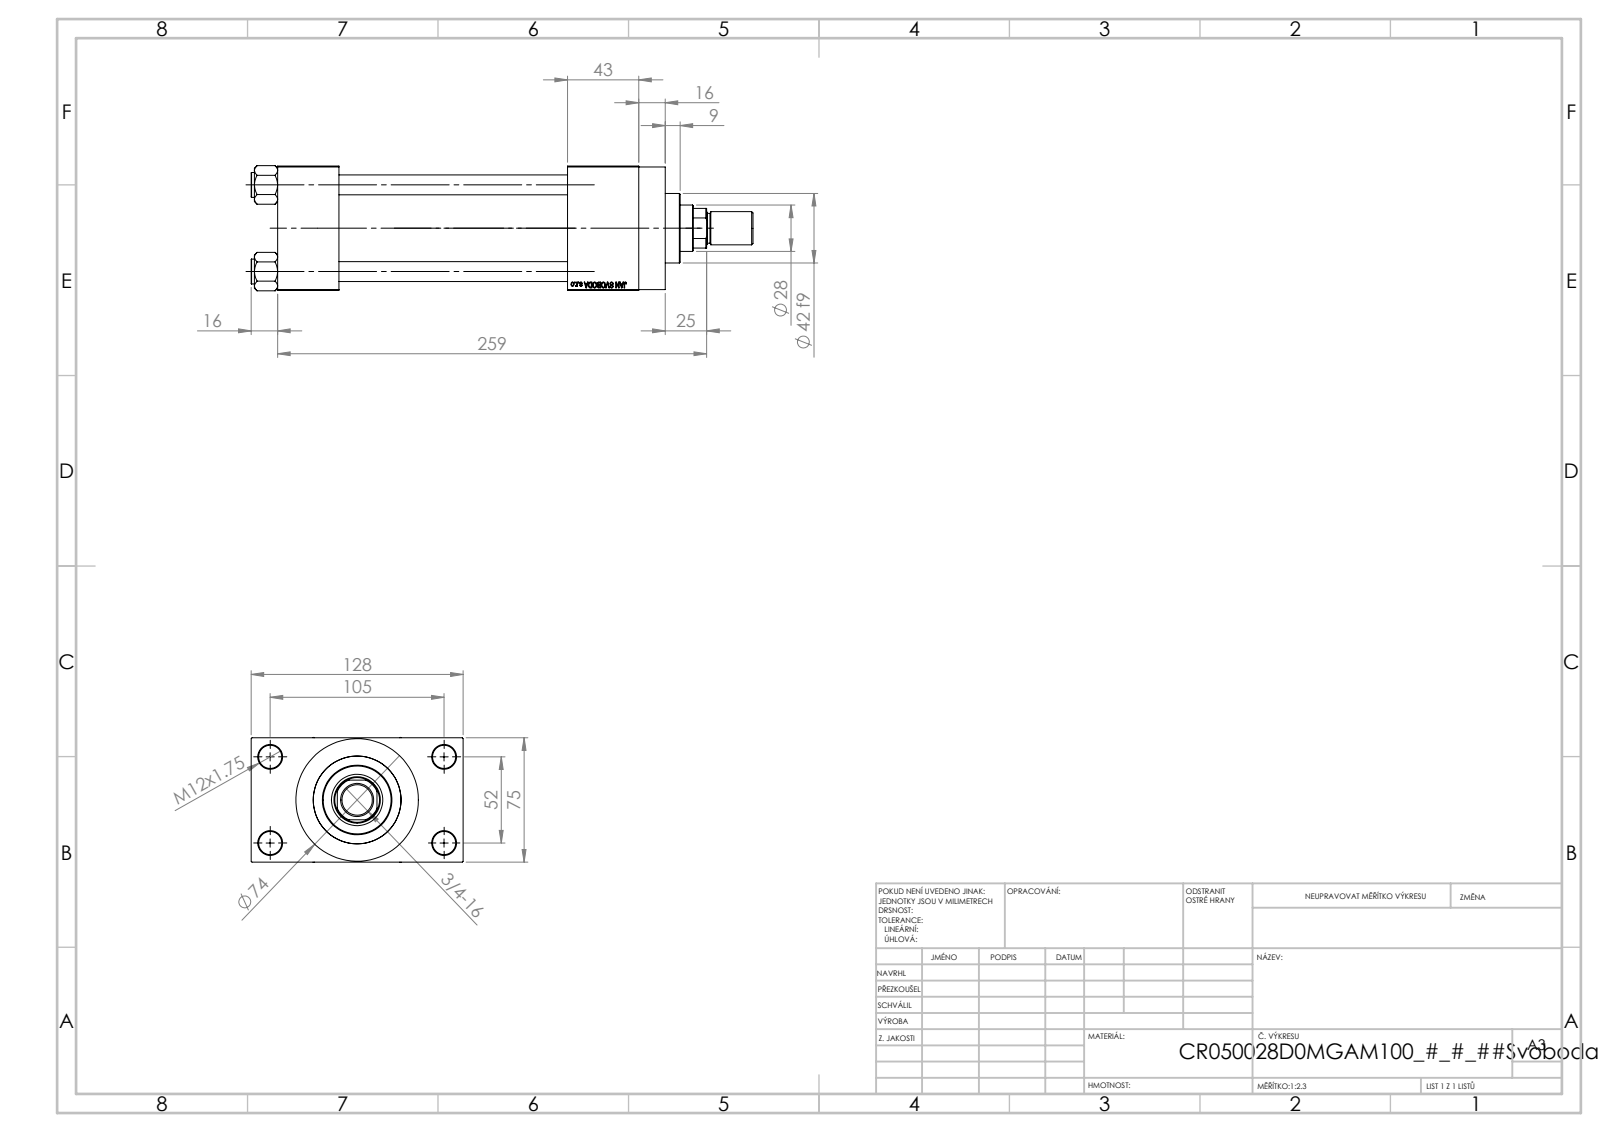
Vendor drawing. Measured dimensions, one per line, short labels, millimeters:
name: V215CR_D_Body; V215CR_VCP_D; V215CR_D_TYCINKA; ROD_END_AH (+2 more)
written by: SolidWorks 2019 (CONFIG_CONTROL_DESIGN)
unit: mm
bodies: 12 solids, 1118 faces (501 planar, 93 cylindrical, 524 other)
size: 303 × 128 × 75.54
volume: 949 296 mm³; area: 217 043 mm²
holes: 4× ⌀12, 4× ⌀14, 2× ⌀7, 2× ⌀20.96, 2× ⌀30, 1× ⌀18.5, 1× ⌀28, 1× ⌀31, 1× ⌀41, 1× ⌀50, 1× ⌀53
bosses: 4× ⌀15, 1× ⌀74, 1× ⌀56, 1× ⌀42, 1× ⌀20, 1× ⌀18
rounds: 1× R13.5
face distances: 75, 138, 37, 175, 26.5, 101.5, 218, 181, 43, 16
hole spacings: 26.35, 36.98, 52.3, 58.43, 58.59, 78.65, 94.37, 52
